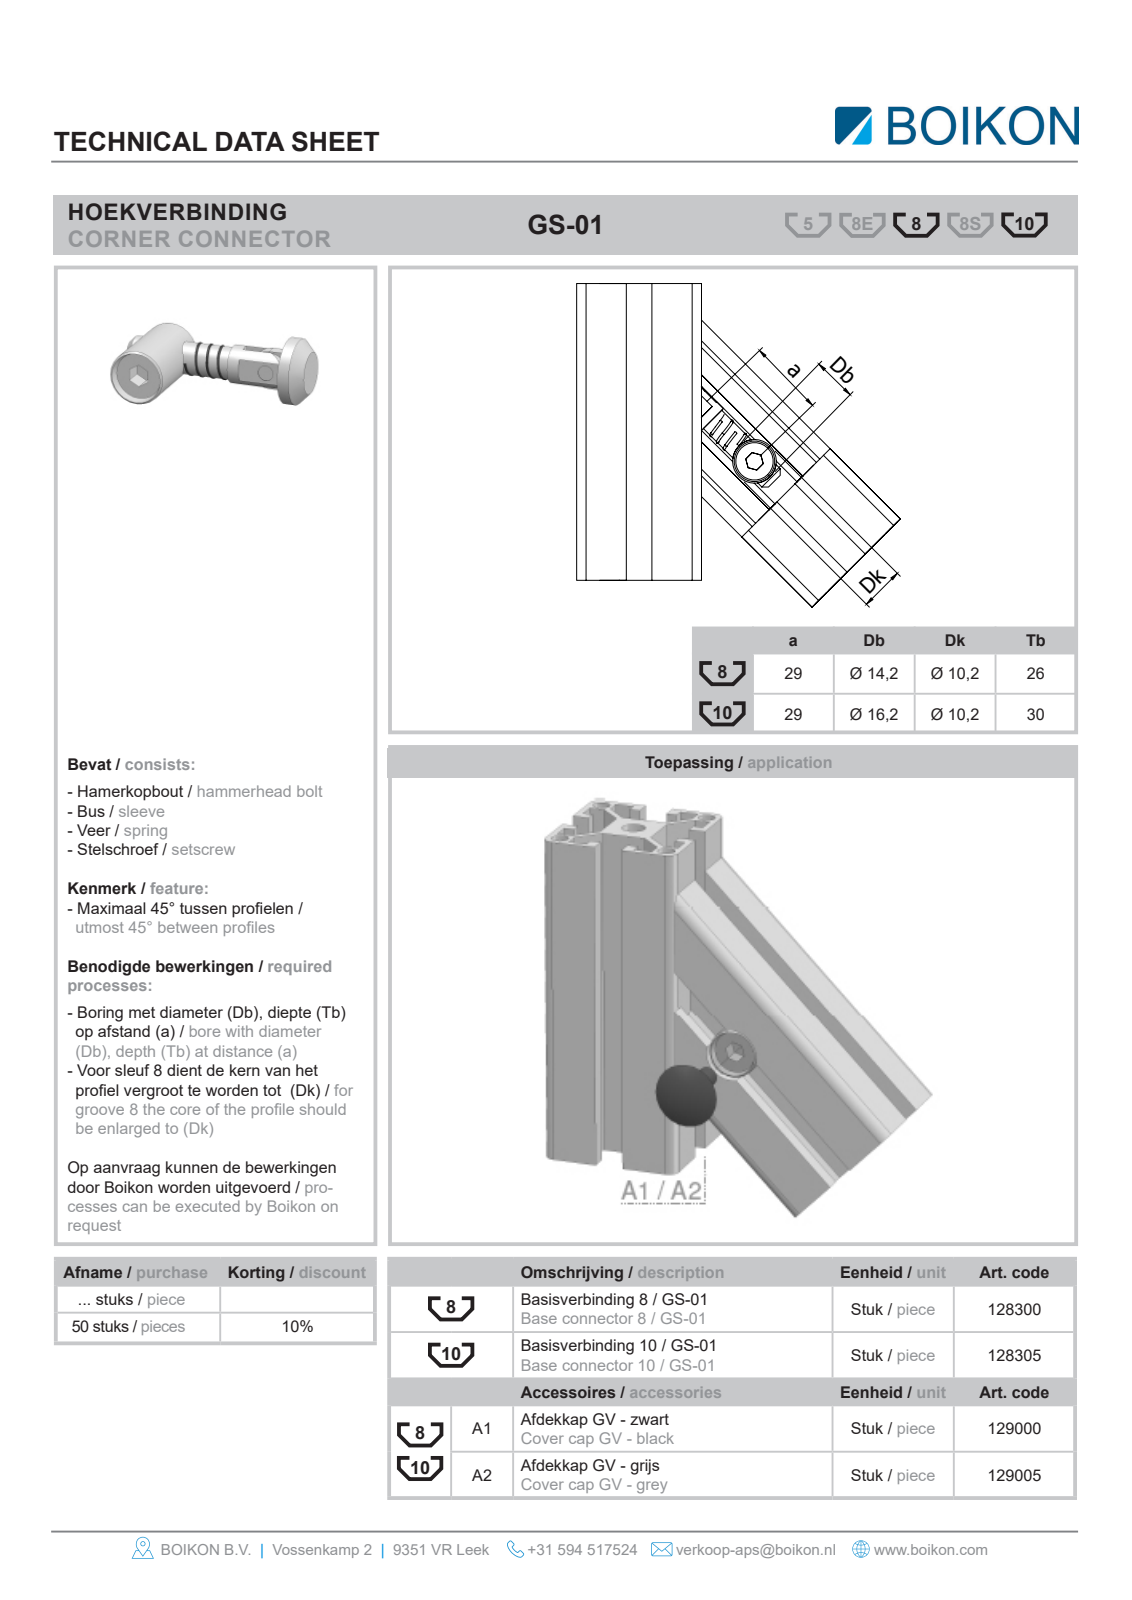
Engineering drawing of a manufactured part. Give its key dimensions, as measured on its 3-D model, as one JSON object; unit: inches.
{"part_name": "Root; 128300Hoekverbinding 8 / GS-01BOIKON", "step_written_by": "HiCAD 2013 1802.4 Build 509 (AUTOMOTIVE_DESIGN)", "units": "inches", "bodies": {"solids": 2, "faces": 44, "planar": 28, "cylindrical": 14, "other": 2}, "overall_size": [1.913, 1.083, 0.669], "volume_in3": 0.387, "surface_area_in2": 5.264, "round_holes": [[0.157, 1]], "round_bosses_or_shafts": [[0.669, 1], [0.551, 1], [0.386, 1], [0.327, 1]], "partial_cylinders_radius": [[0.185, 1], [0.197, 1]], "face_to_face_distances": [0.116, 0.945, 0.118, 0.256, 0.098, 0.1, 0.215, 0.217, 0.232, 0.138]}
